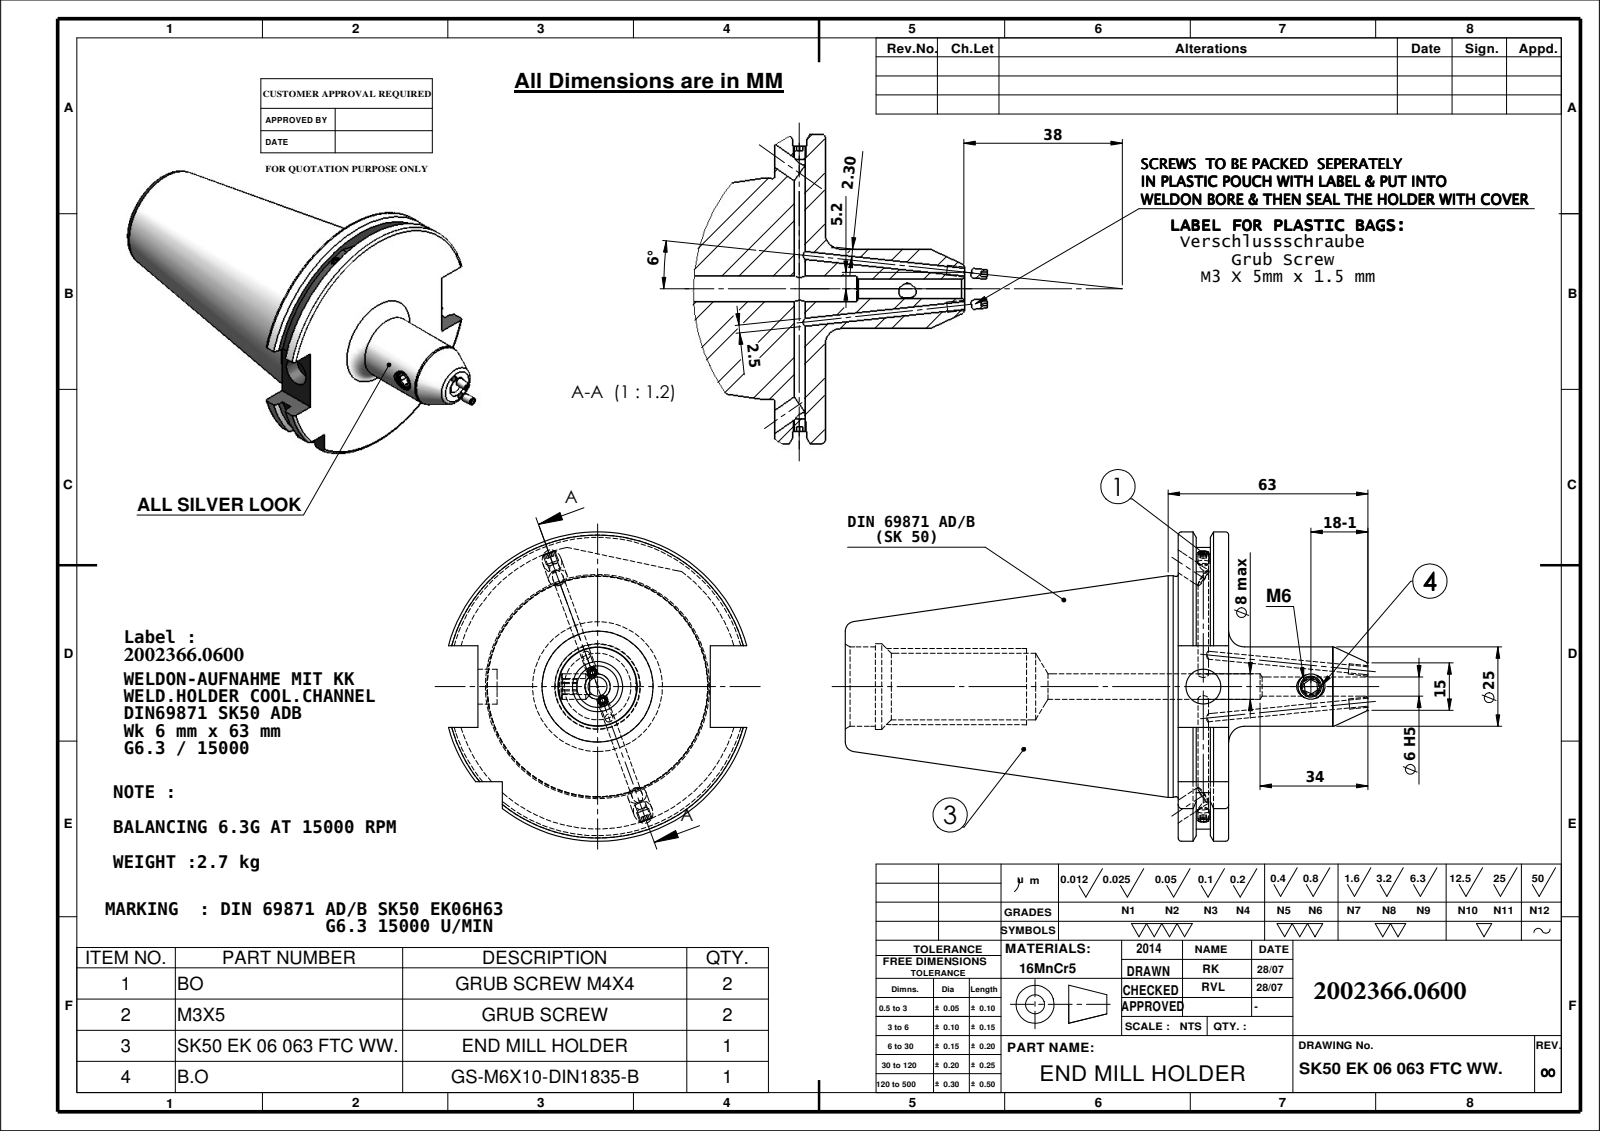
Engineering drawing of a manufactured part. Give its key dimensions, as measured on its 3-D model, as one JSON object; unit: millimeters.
{"part_name": "M6X10._DIN 913 - M8 x 8-N; SK50 EK 06 063 FTC WW.; M3X5_DIN 913 - M3 x 5-N; Copy of M4X4_DIN 913 - M4 x 4-N", "step_written_by": "SolidWorks 2009 (CONFIG_CONTROL_DESIGN)", "units": "millimeters", "bodies": {"solids": 6, "faces": 200, "planar": 69, "cylindrical": 61, "other": 70}, "overall_size": [172.02, 97.5, 94.05], "volume_mm3": 353595, "surface_area_mm2": 48359, "round_holes": [[6, 3], [2.5, 2], [8, 2], [3.3, 1], [5, 1], [11, 1], [21, 1], [25, 1], [27, 1]], "round_bosses_or_shafts": [[4, 2], [3, 2], [69.85, 1], [69.45, 1]], "partial_cylinders_radius": [[44.9, 1], [48.75, 1]], "face_to_face_distances": [15.9, 10.15, 5.75, 5.66, 4.49, 10.24, 104.95, 110.61, 115.1, 120.85], "hole_center_spacings": [33.9]}
